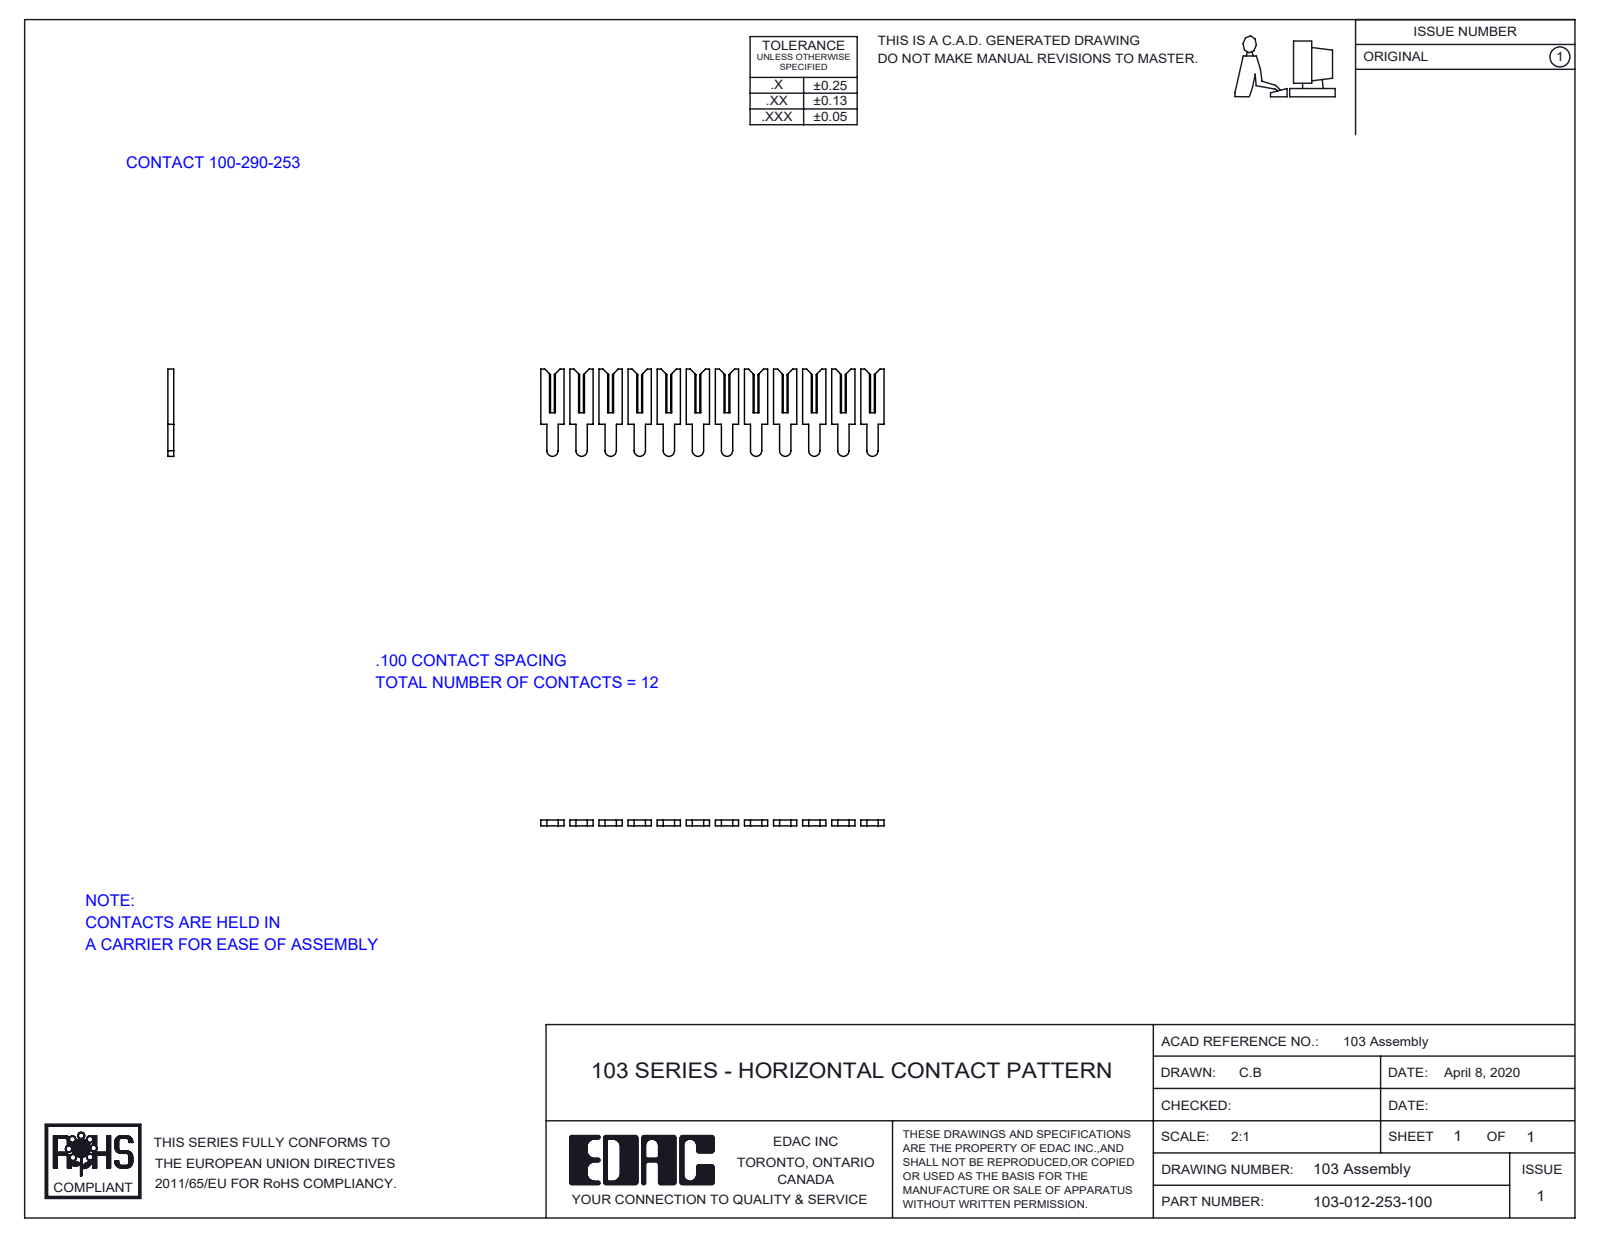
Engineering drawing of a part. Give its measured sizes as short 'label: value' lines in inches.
name: 100-290-001_100-290-253; 103-012-253-100
written by: SolidWorks 2016 (CONFIG_CONTROL_DESIGN)
unit: in
bodies: 12 solids, 240 faces (228 planar, 12 cylindrical, 0 other)
size: 1.18 × 0.3 × 0.02
volume: 0.004 in³; area: 0.64 in²
rounds: 12× R0.019
face distances: 0.02, 0.1, 0.2, 0.3, 0.4, 0.5, 0.141, 0.6, 0.08, 0.18
